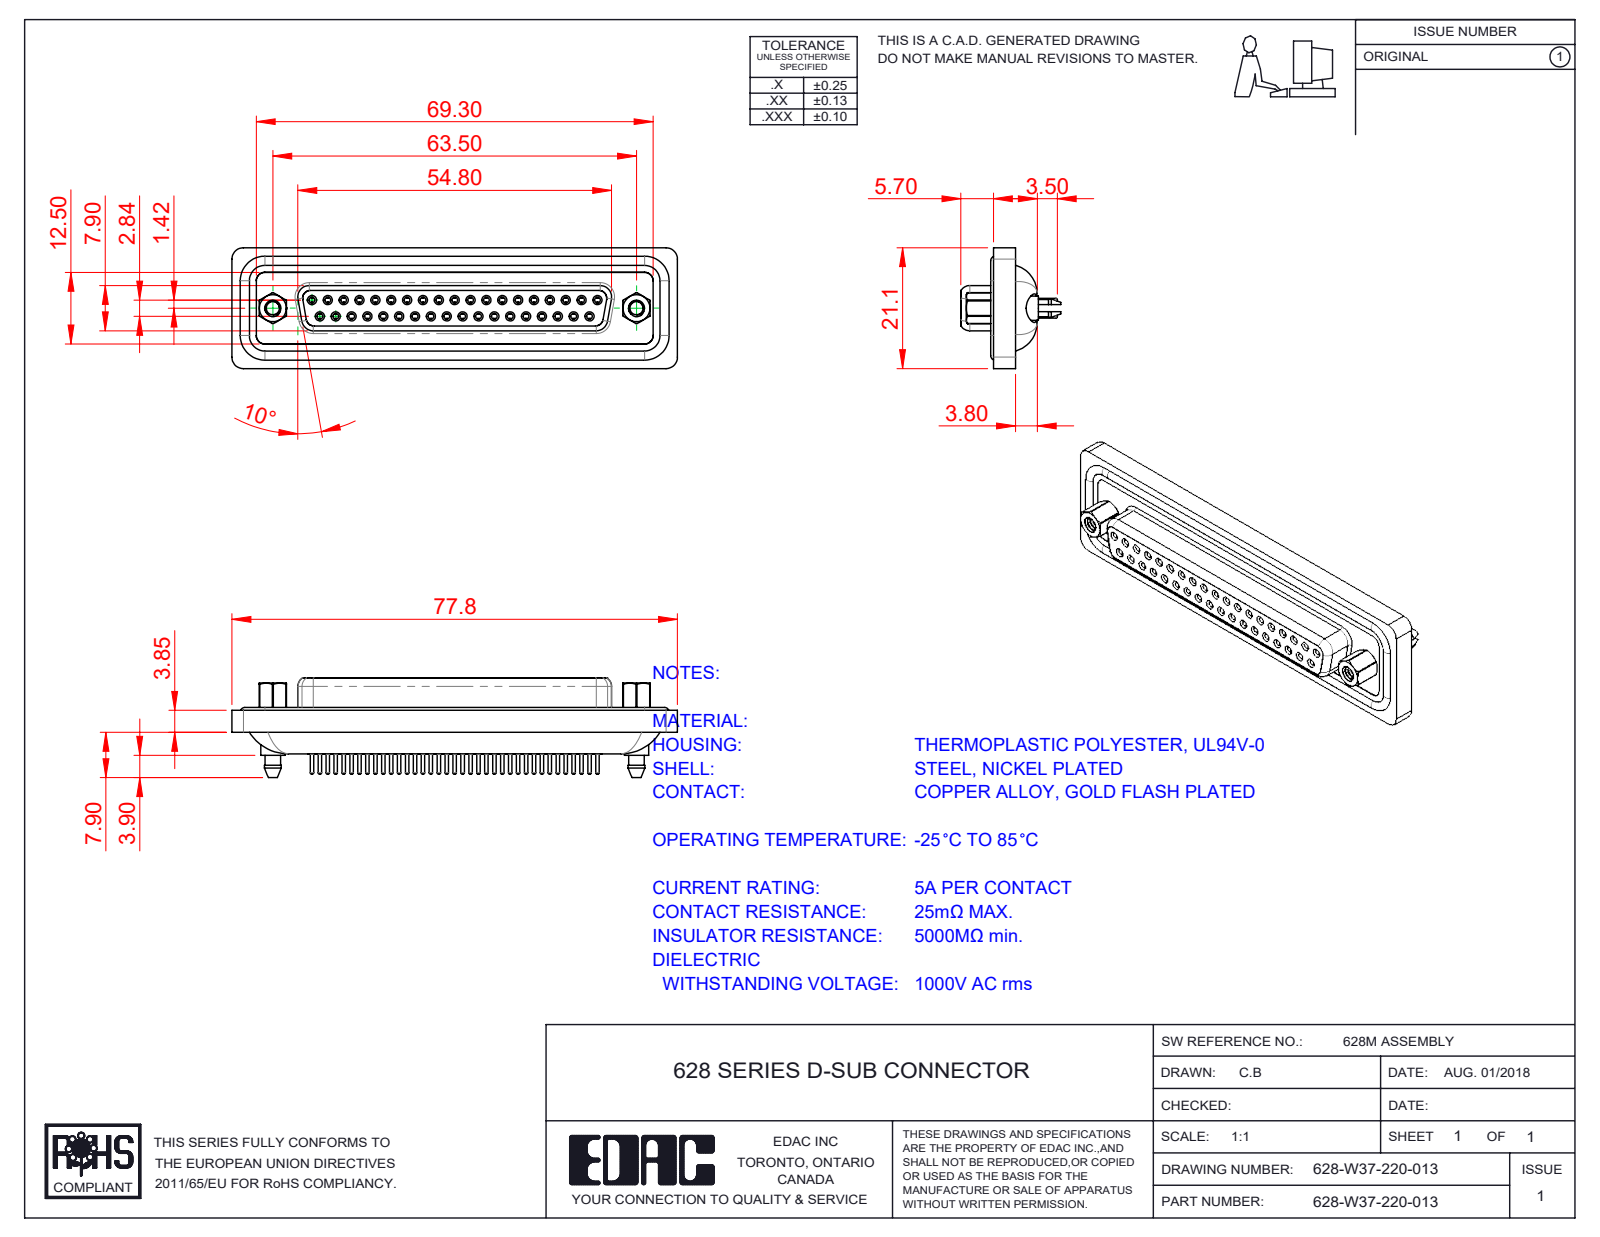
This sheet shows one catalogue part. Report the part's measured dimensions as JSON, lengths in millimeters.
{"part_name": "628W 4-40 Threaded Boardlock; 628W Shell Front_37 Contacts; 628W Housing_37 Contacts; 628-W37-220-013 (+4 more)", "step_written_by": "SolidWorks 2020 (CONFIG_CONTROL_DESIGN)", "units": "millimeters", "bodies": {"solids": 45, "faces": 2580, "planar": 670, "cylindrical": 1029, "other": 881}, "overall_size": [77.8, 21.1, 17.45], "volume_mm3": 11033, "surface_area_mm2": 18127, "round_holes": [[1, 37], [1.1, 37], [1.5, 37], [1.7, 37], [1.8, 37], [2, 37], [2.26, 2], [2.29, 2], [4, 2], [4.8, 2], [5, 2]], "round_bosses_or_shafts": [[1.6, 41], [2.2, 37], [0.6, 37], [1.5, 8], [5.4, 2], [4.9, 2], [4.25, 2], [2.79, 2]], "partial_cylinders_radius": [[1.5, 16], [2, 16], [1.35, 8], [1.6, 6], [0.5, 4], [0.9, 4], [1.75, 4], [2.7, 4]], "face_to_face_distances": [0.4, 7.45, 7.5, 8.45, 6.2, 13.65, 3.75, 4.1, 5.65, 1.1], "hole_center_spacings": [3.16, 2.77, 5.54, 8.31, 5.04, 7.49, 11.08, 13.85]}
